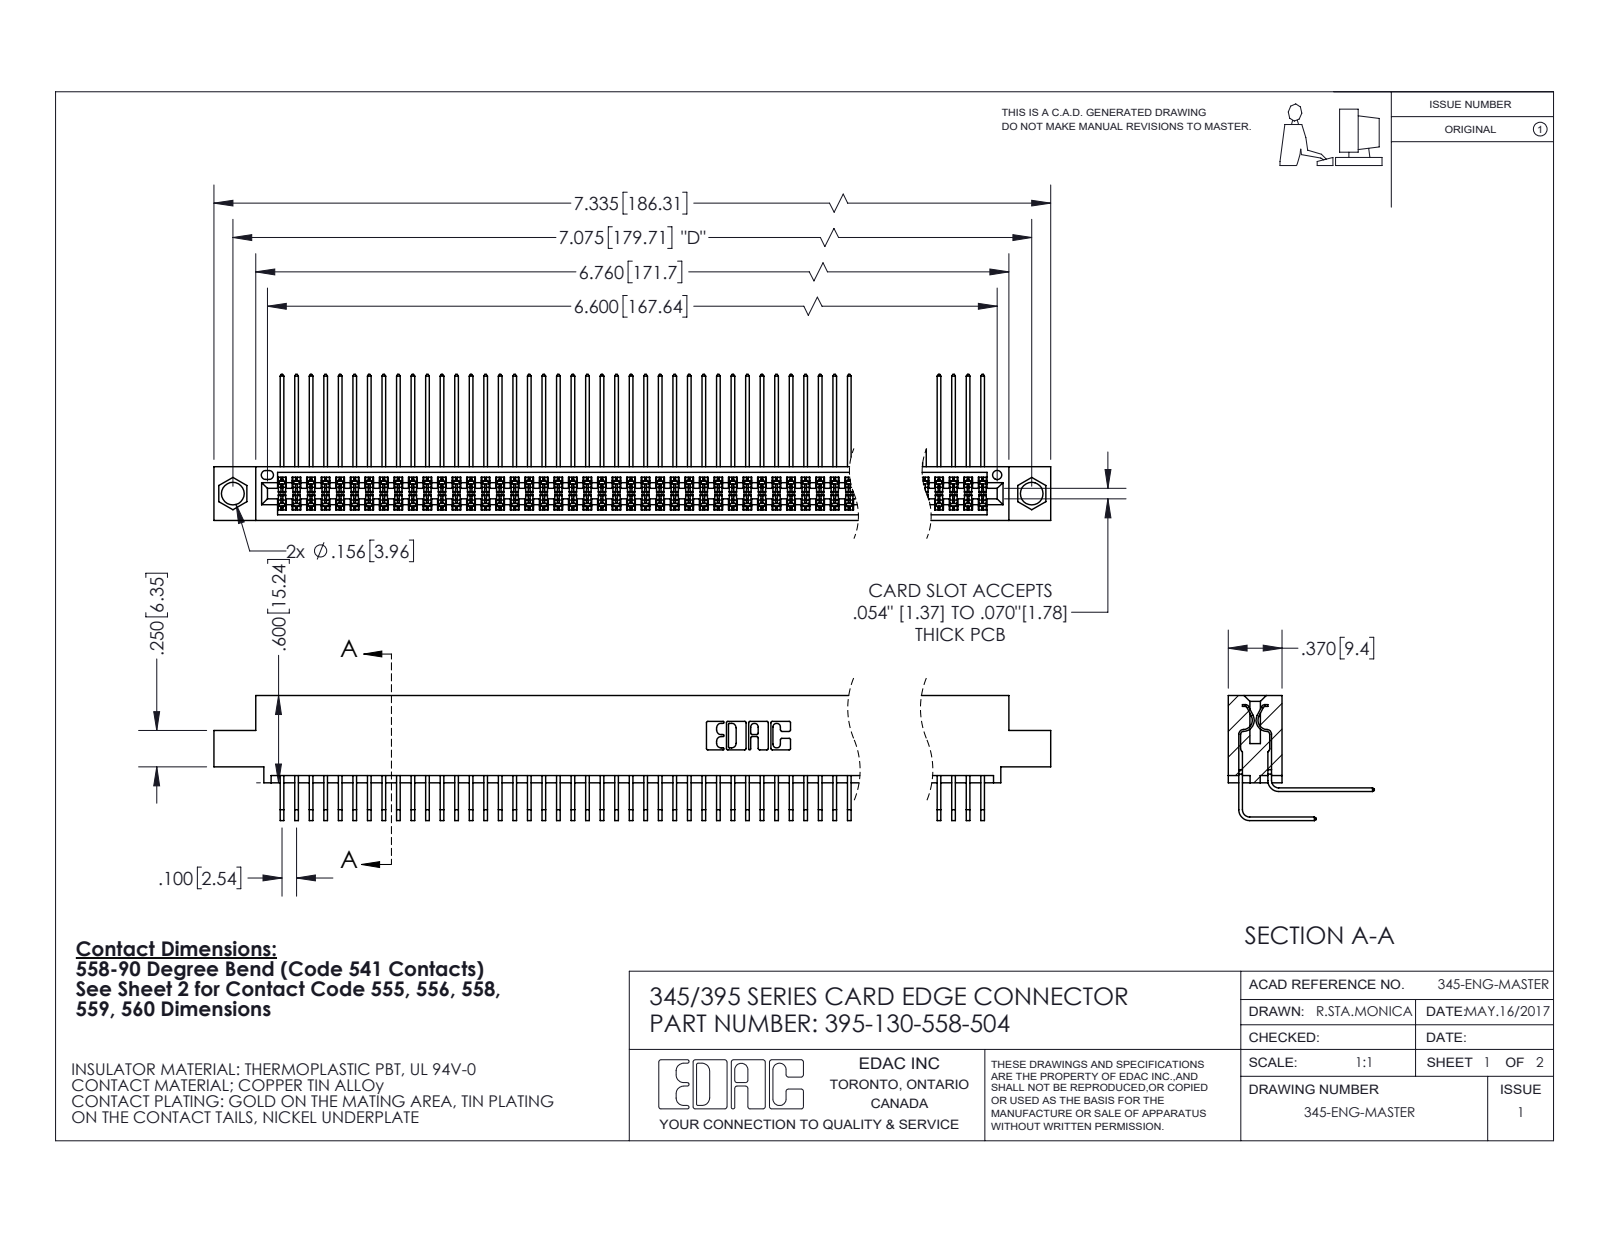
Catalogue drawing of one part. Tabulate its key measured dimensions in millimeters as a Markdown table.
| quantity | value |
| --- | --- |
| part name | 345-292-001_558 559 Tail - 1; 395-130-558-504; 345-292-001_558 Tail - 2; 345 Part_0.110 Offset - 0.156 Dia-TI |
| STEP written by | SolidWorks 2020 (CONFIG_CONTROL_DESIGN) |
| units | millimeters |
| bodies | 131 solids, 6904 faces (4648 planar, 2256 cylindrical, 0 other) |
| overall size | 186.3 × 25.5 × 21.8 |
| volume | 18 880 mm³ |
| surface area | 31 830 mm² |
| round holes (diameter × count) | 4 × 2, 1.6 × 1 |
| partial cylindrical surfaces (radius × count) | 0.2 × 195, 0.3 × 22, 0.2 × 6, 0.8 × 6, 0.7 × 3, 0.4 × 2, 0.5 × 2, 0.6 × 2 |
| main face-to-face distances | 1.8, 7.6, 5.1, 9.4, 2.5, 6.9, 0.6, 5.7, 0.6, 4.4 |
| hole center spacings | 6.9, 173.7, 179.7 |
